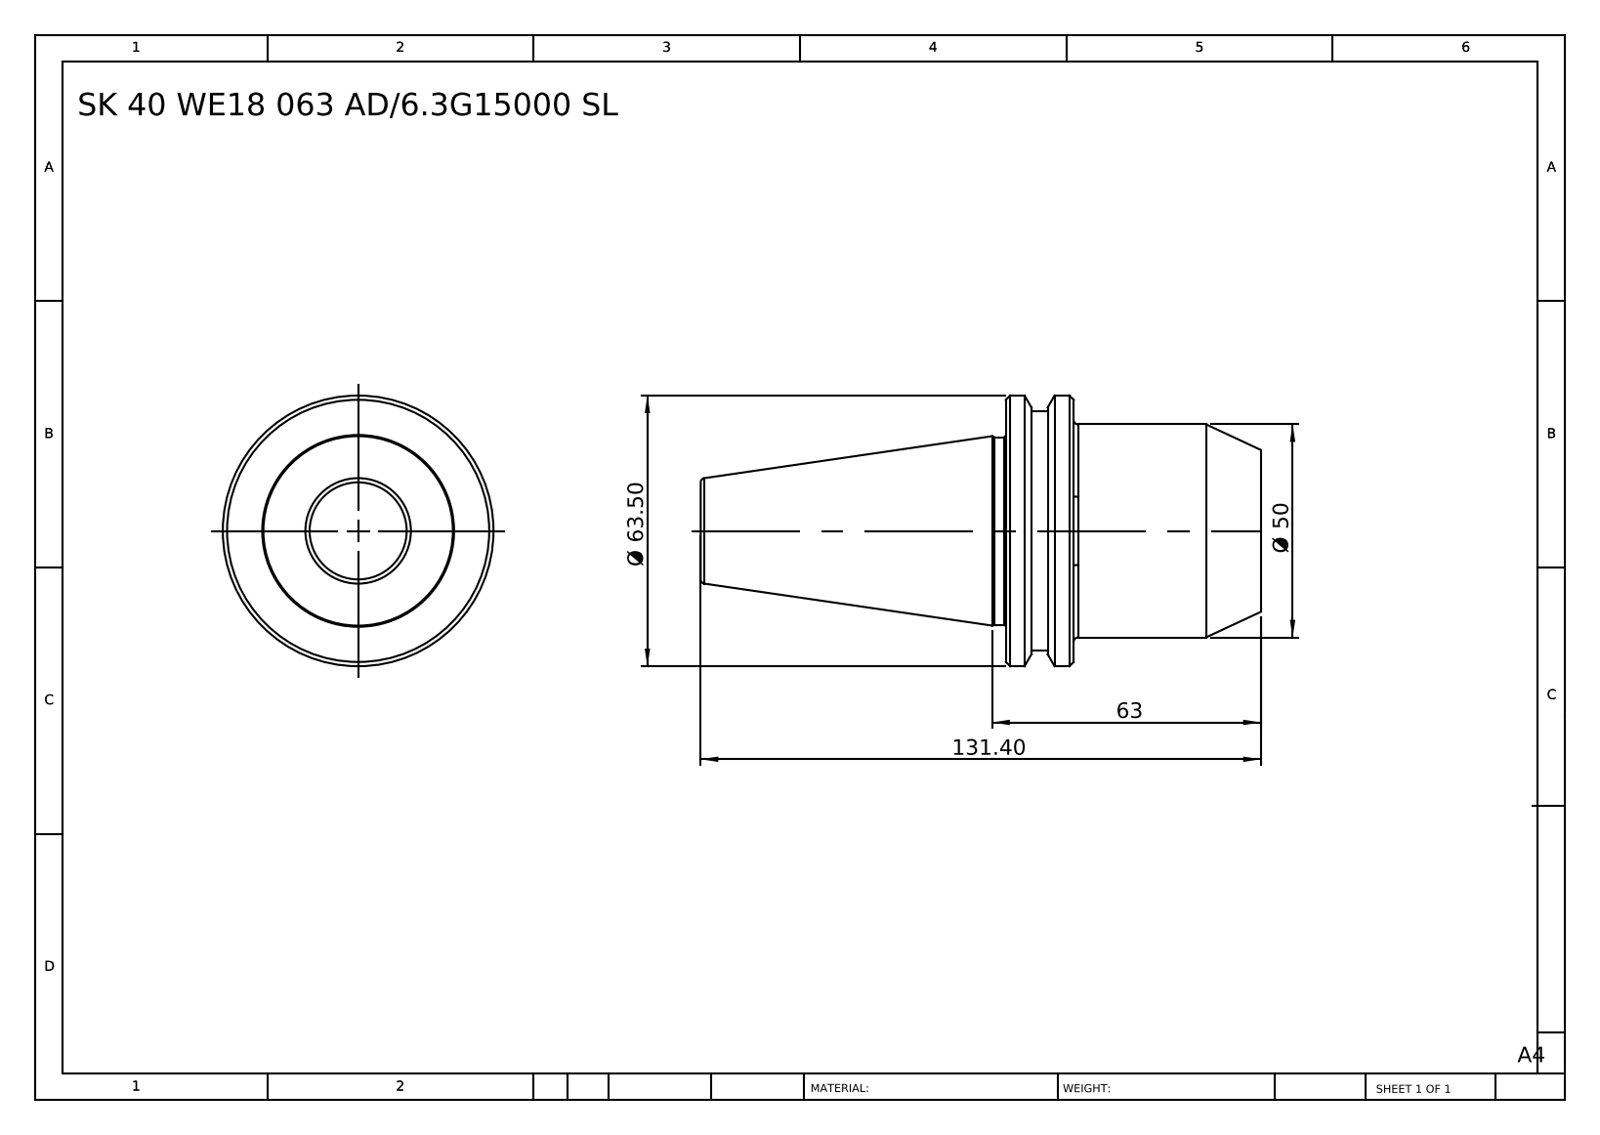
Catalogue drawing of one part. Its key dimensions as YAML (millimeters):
part_name: "SK40 WE18 063 AD-6.3G15000 SL"
step_written_by: "SolidWorks 2014 (CONFIG_CONTROL_DESIGN)"
units: millimeters
bodies: {solids: 1, faces: 36, planar: 6, cylindrical: 10, other: 20}
overall_size: [131.4, 63.5, 63.5]
volume: 197759
surface_area: 22883
round_bosses_or_shafts:
  - {diameter: 63.5, count: 1}
  - {diameter: 56, count: 1}
  - {diameter: 50, count: 1}
  - {diameter: 44, count: 1}
face_to_face_distances: [59.8, 43.9, 15.9, 131.4, 87.5, 71.6, 50, 6.1, 9.8, 81.4]
